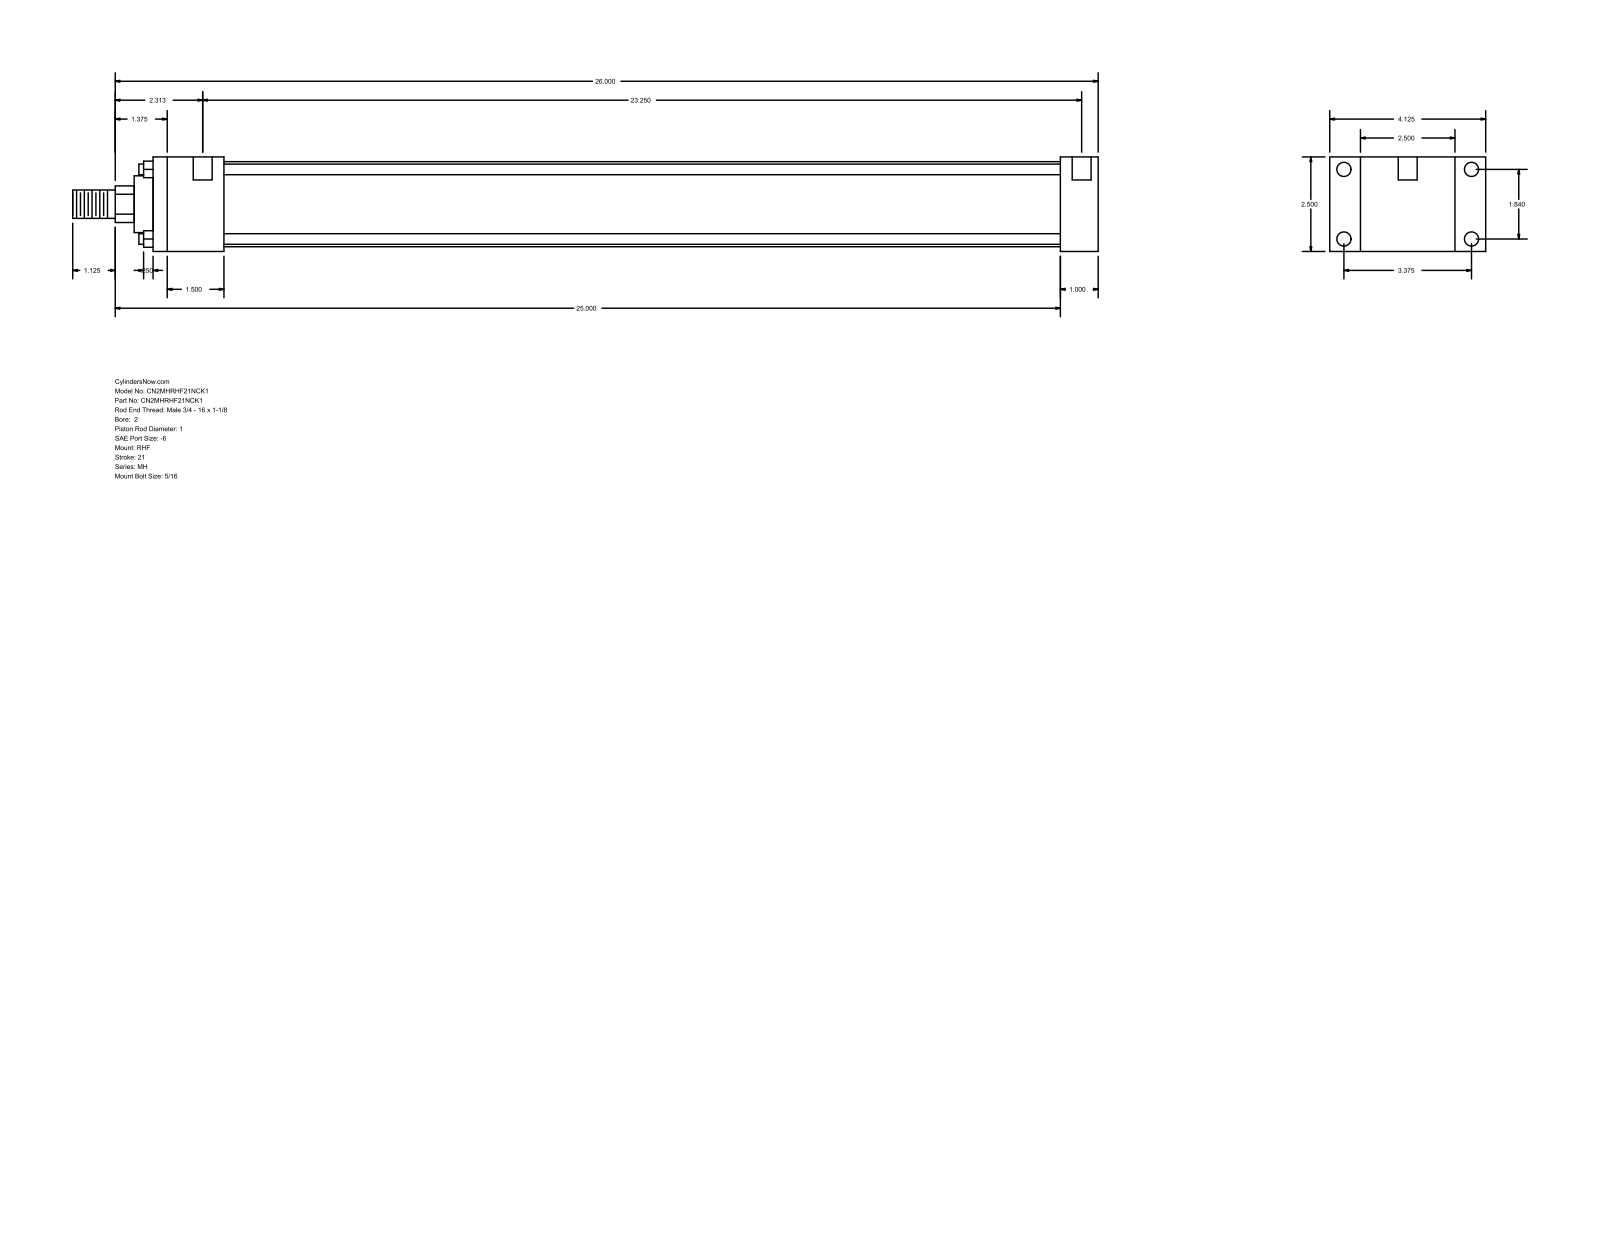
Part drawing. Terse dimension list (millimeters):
name: MH_RHF__0200_1
written by: GSSL Pune (CONFIG_CONTROL_DESIGN)
unit: mm
bodies: 0 solids, 88 faces (60 planar, 28 cylindrical, 0 other)
size: 688.98 × 104.78 × 63.5
holes: 4× ⌀5.56, 4× ⌀9.53, 2× ⌀12.7
bosses: 4× ⌀7.14, 1× ⌀57.15, 1× ⌀38.1, 1× ⌀25.4, 1× ⌀19.05
rounds: 1× R12.29
face distances: 63.5, 25.4, 20.64, 84.14, 635, 609.6, 104.78, 47.63, 561.97, 587.37
hole spacings: 46.74, 85.72, 97.63, 598.48, 3.17, 4.76, 590.55, 593.72
